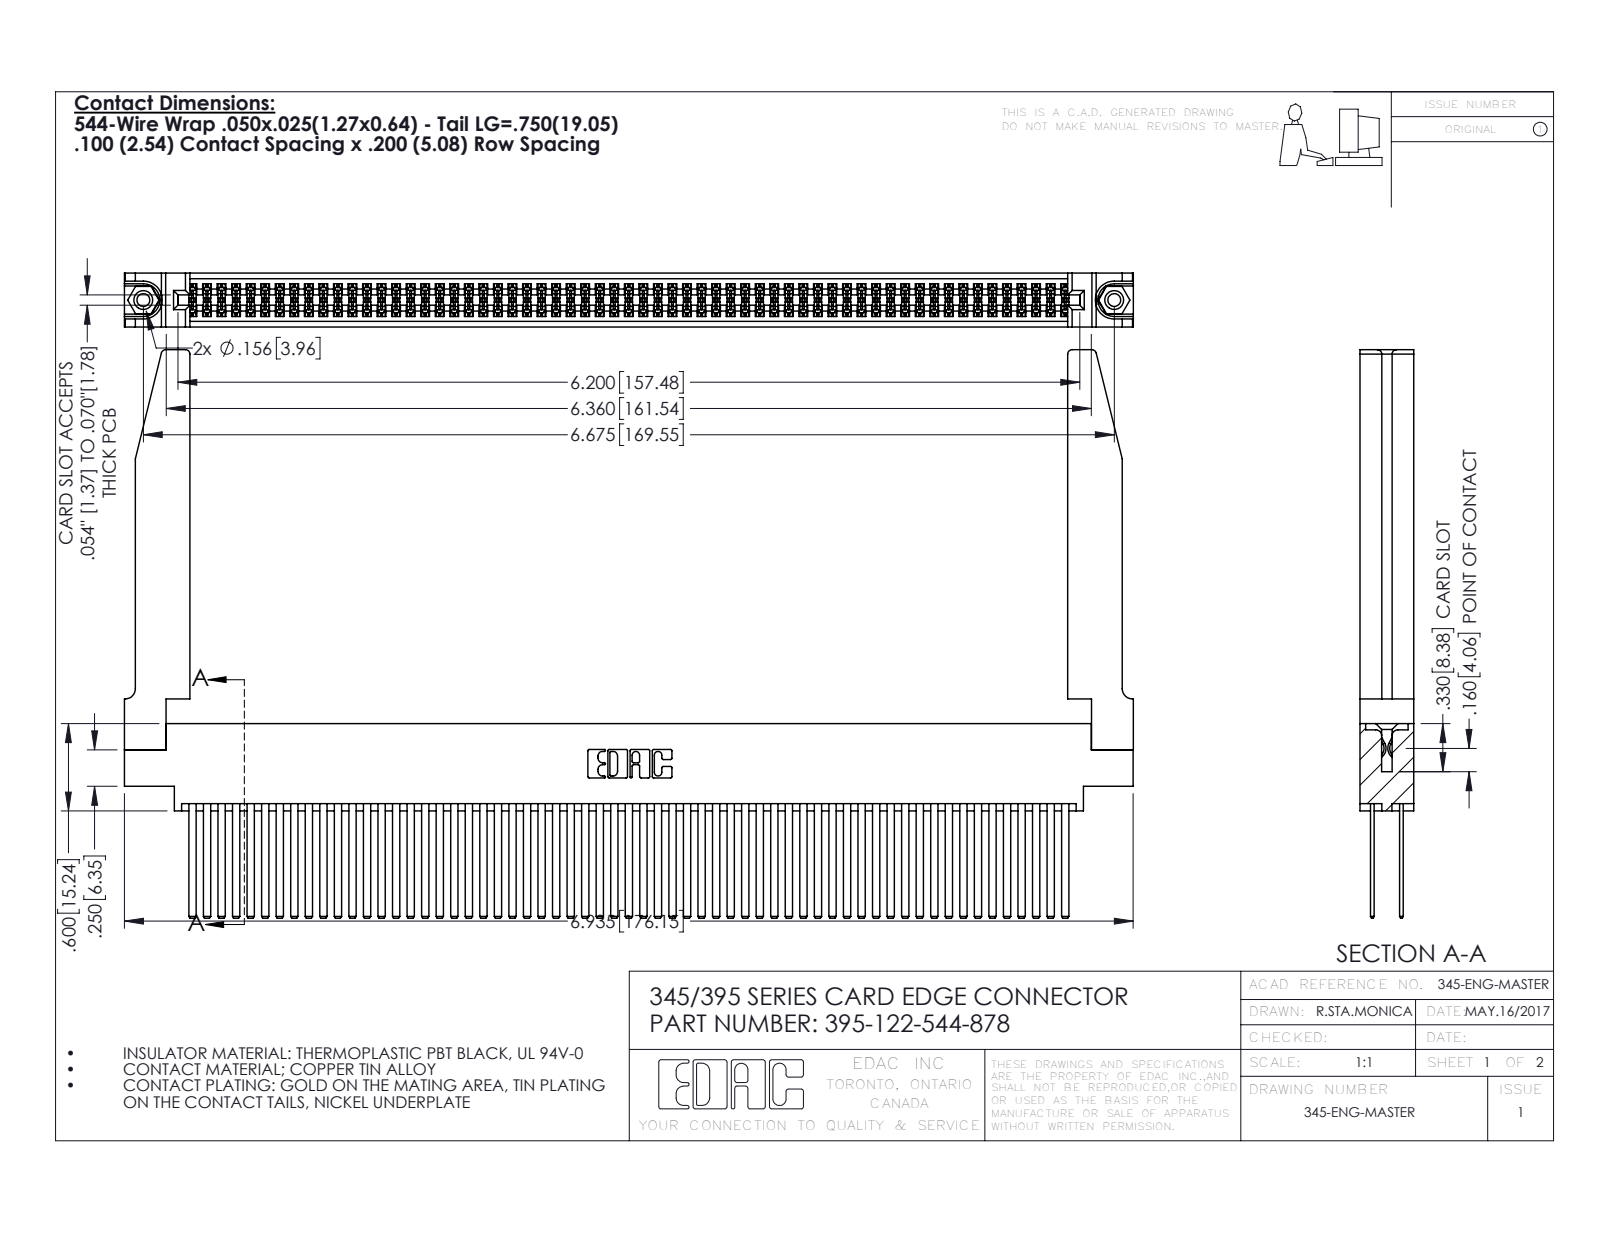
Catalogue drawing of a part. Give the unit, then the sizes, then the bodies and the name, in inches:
Units: inches
Overall size (bounding box): 6.936 × 3.907 × 0.37
Round holes (diameter × count): ⌀0.089 ×2, ⌀0.125 ×2, ⌀0.156 ×2, ⌀0.064 ×1
Round bosses / shafts (diameter × count): ⌀0.155 ×2
Partial cylindrical surfaces — rounded edges, fillets, slot ends (radius × count): R0.006 ×183, R0.01 ×22, R0.03 ×8, R0.007 ×6, R0.031 ×6, R0.026 ×3, R0.014 ×2, R0.019 ×2
Main face-to-face distances: 0.072, 0.298, 0.098, 0.272, 0.025, 0.2, 0.37, 0.225, 0.175, 0.148
Hole centre spacings: 0.27, 6.439, 6.675
Volume: 1.627 in³ · Surface area: 62.43 in²
Bodies: 127 solids, 5732 faces (3764 planar, 1916 cylindrical, 52 other)
Part name (STEP PRODUCT): 345-220-078_345-220-078; 345 Part_0.170 Offset - 0.156 Dia-TH; 395-122-544-878; 345-250-001_345-250-001-102 (+1 more)
STEP written by: SolidWorks 2016 (CONFIG_CONTROL_DESIGN)
